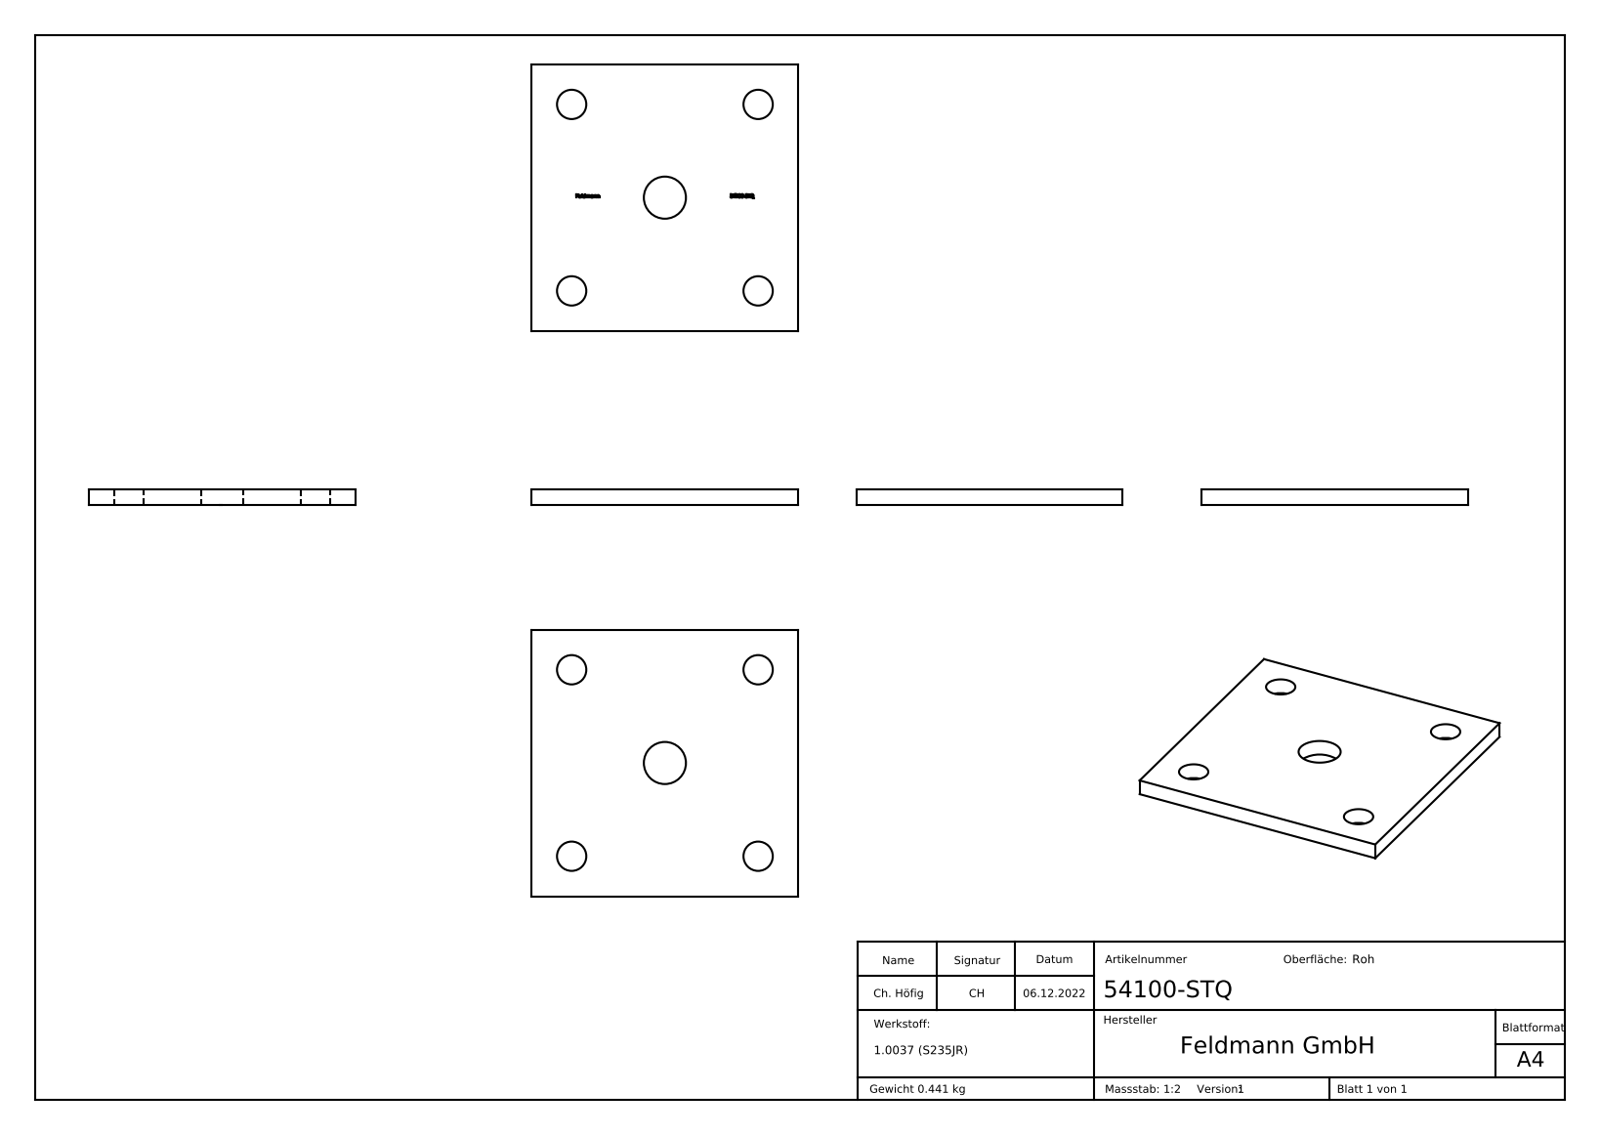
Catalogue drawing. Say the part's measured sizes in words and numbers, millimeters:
The part is named "54100-STQ". Its 3-D file was written by "SolidWorks 2018 (CONFIG_CONTROL_DESIGN)". It is 1 solid with 233 faces: 129 planar, 5 cylindrical and 99 other. Overall it measures 100 by 100 by 6 millimeters. Its volume is 56 542 cubic millimeters and its surface area 22 384 square millimeters. Round holes: 4 of diameter 11, 1 of diameter 15.8. The main face-to-face distances are 6, 100, 5.9, 50, 58.18, 64.62, 1.32, 51.32, 48.68, 5.22. The hole center spacings are 49.5, 70, 98.99.
